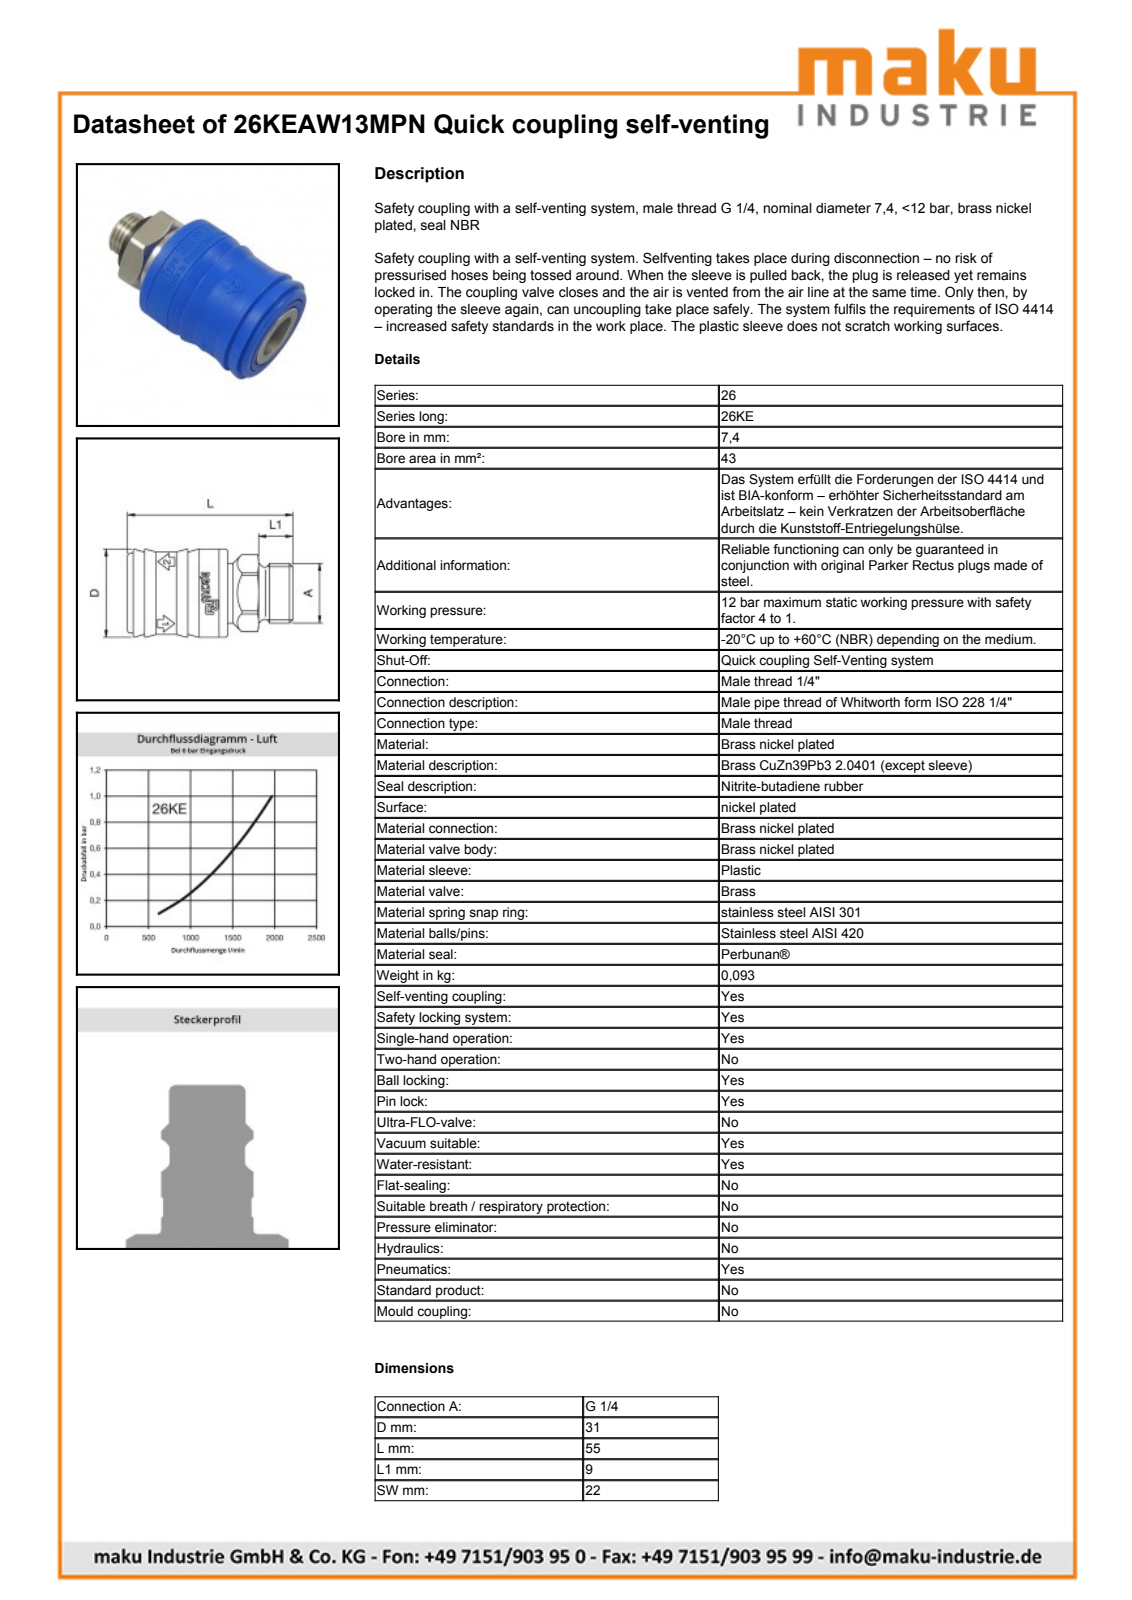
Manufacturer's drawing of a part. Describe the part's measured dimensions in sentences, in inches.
The part is named "D103604". Its 3-D file was written by "Autodesk Inventor 2011 (AUTOMOTIVE_DESIGN)". It is 1 solid with 541 faces: 234 planar, 63 cylindrical and 244 other. Overall it measures 2.178 by 1.228 by 1.224 inches. Its volume is 1.717 cubic inches and its surface area 11.94 square inches. Round holes: 1 of diameter 0.569, 1 of diameter 0.573, 1 of diameter 0.669, 1 of diameter 1.142. Round bosses or shafts: 1 of diameter 1.22, 1 of diameter 1.102, 1 of diameter 0.827, 1 of diameter 0.656, 1 of diameter 0.518, 1 of diameter 0.394. Partial cylindrical surfaces (rounded edges, fillets, slot ends): 1 of radius 0.488, 1 of radius 0.614. The main face-to-face distances are 1.268, 1.824, 0.556, 0.866, 0.079, 1.189, 0.354, 1.745, 2.178, 2.1.
